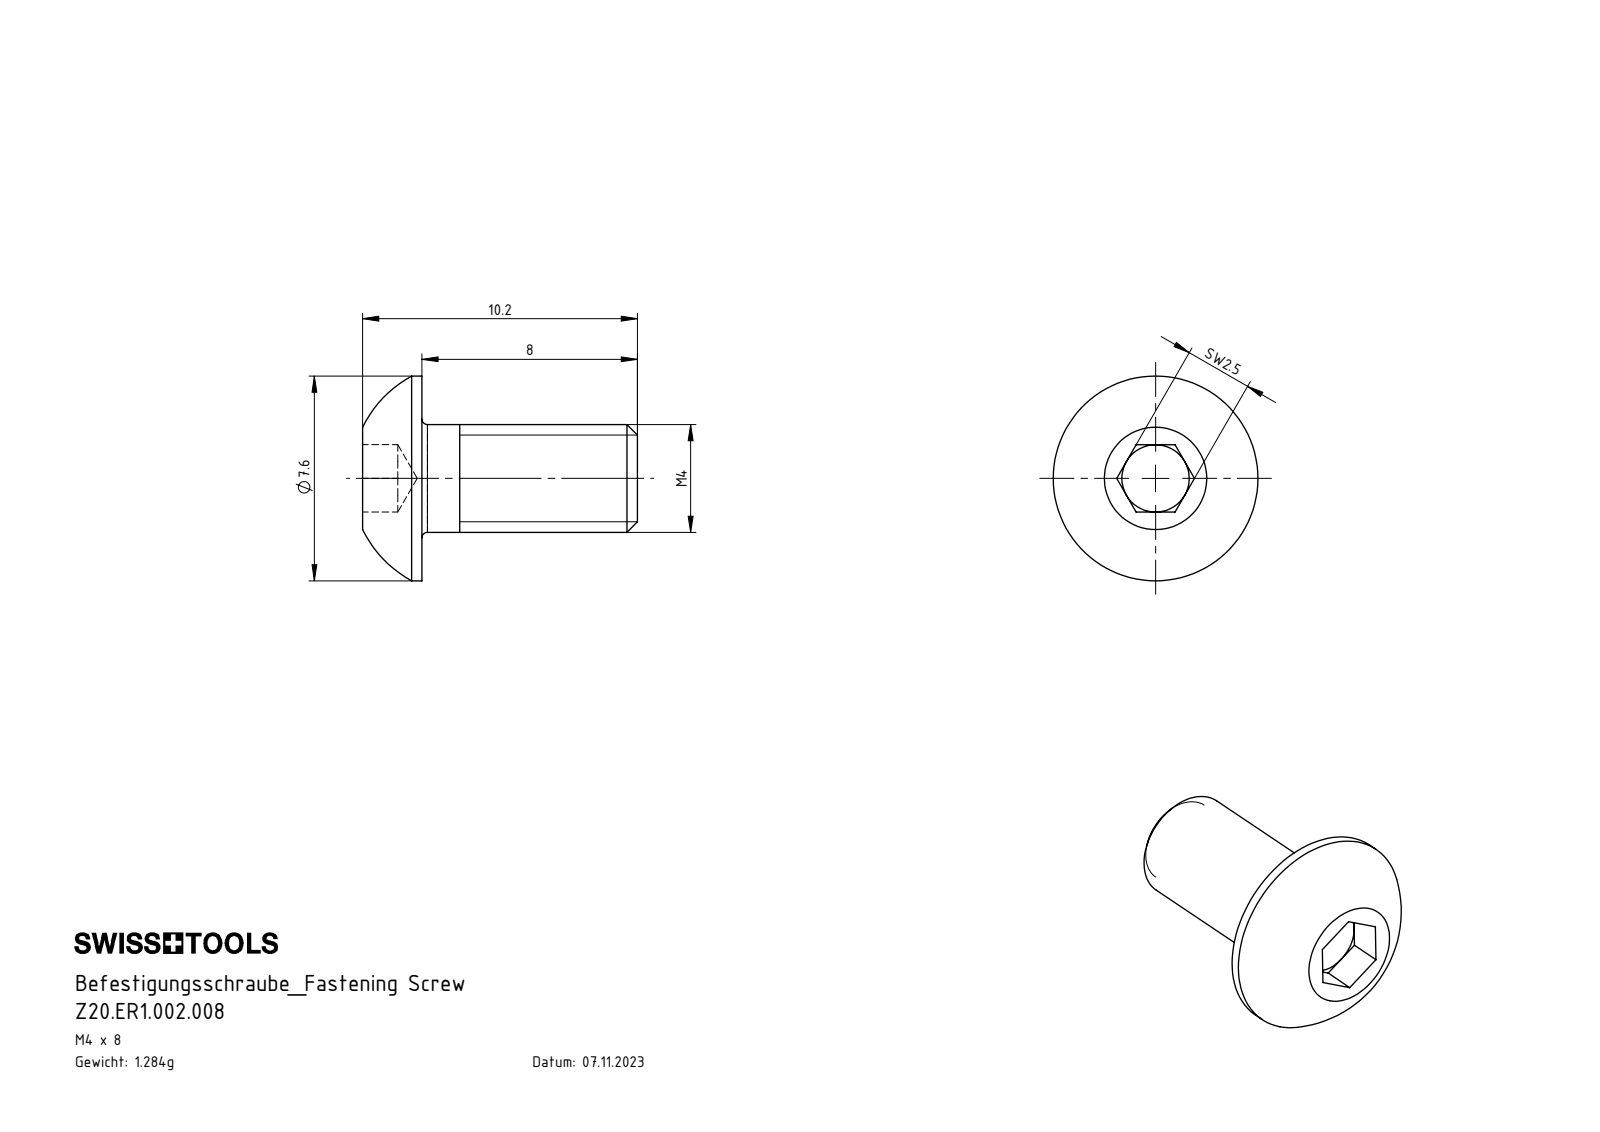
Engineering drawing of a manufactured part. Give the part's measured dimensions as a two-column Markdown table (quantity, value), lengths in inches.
| quantity | value |
| --- | --- |
| part name | Z20.ER1.002.008 |
| STEP written by | SolidWorks 2017 (AUTOMOTIVE_DESIGN) |
| units | inches |
| bodies | 1 solid, 27 faces (15 planar, 4 cylindrical, 8 other) |
| overall size | 0.402 × 0.299 × 0.299 |
| volume | 0.01 in³ |
| surface area | 0.347 in² |
| round bosses / shafts (diameter × count) | 0.299 × 1, 0.157 × 1 |
| main face-to-face distances | 0.315, 0.087, 0.402, 0.098, 0.051, 0.035, 0.35 |
